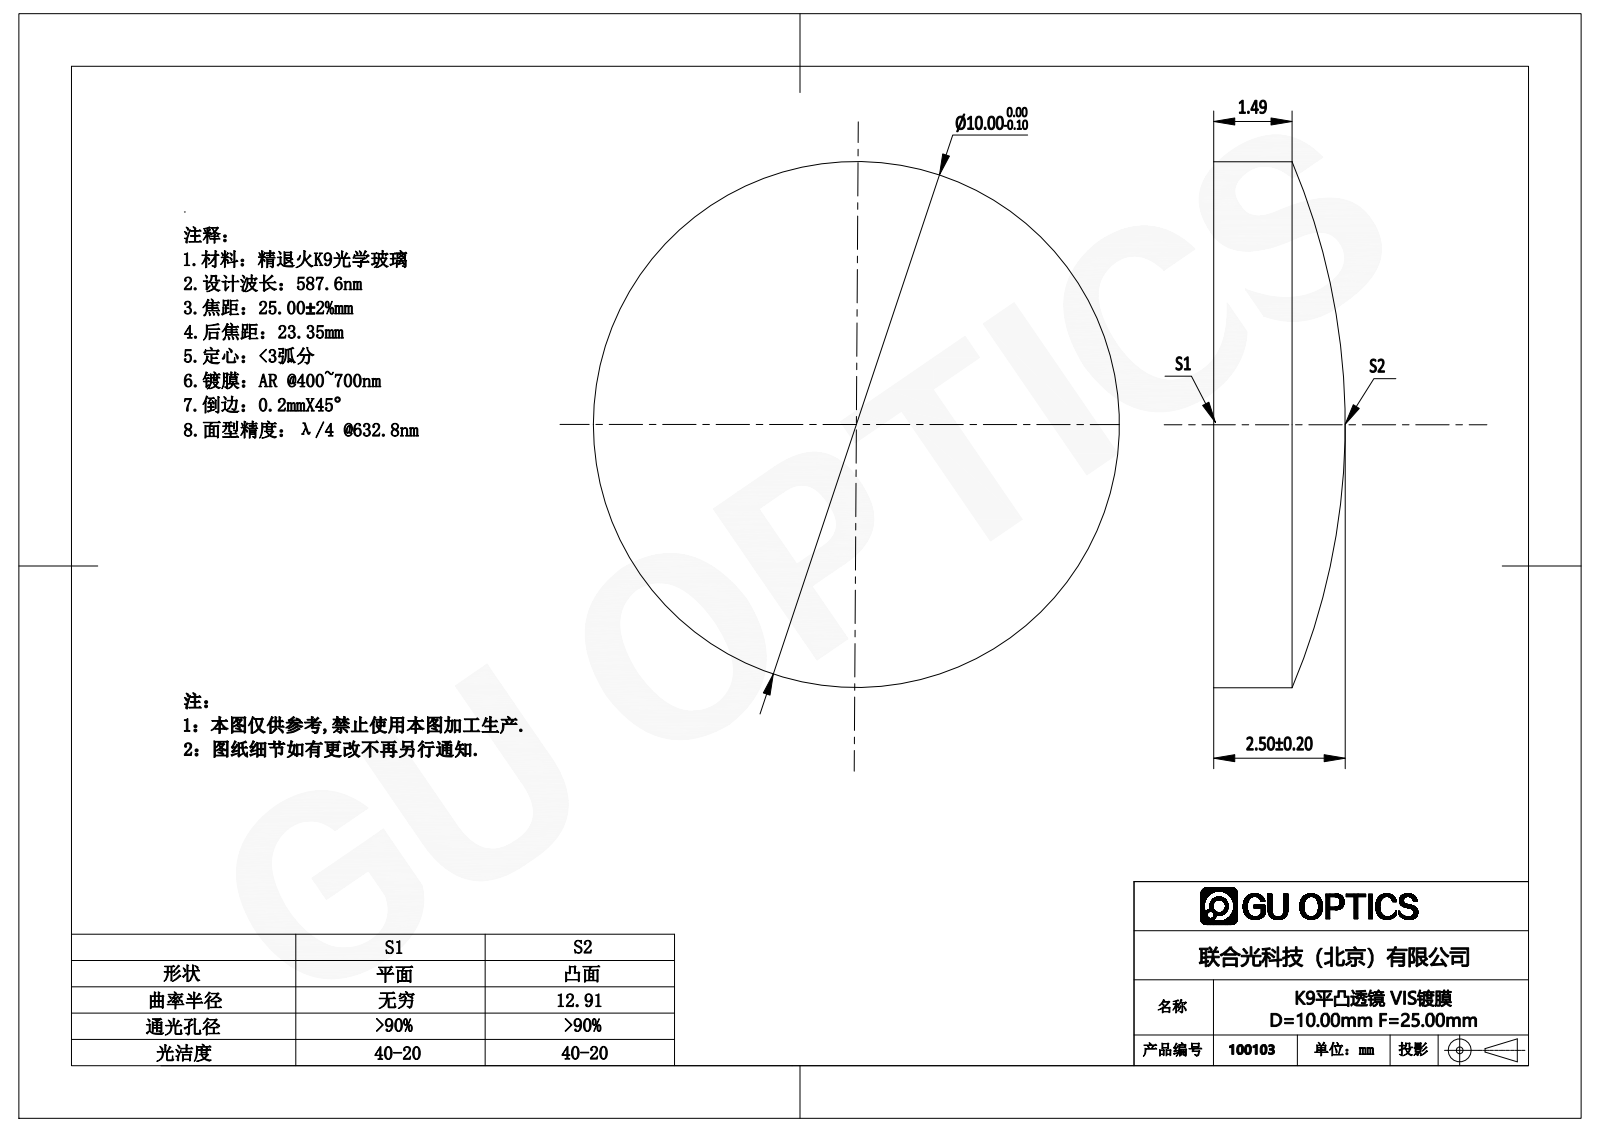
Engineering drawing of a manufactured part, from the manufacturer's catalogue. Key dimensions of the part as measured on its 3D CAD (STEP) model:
Part name (STEP PRODUCT): 100103
STEP written by: SolidWorks 2016 (AUTOMOTIVE_DESIGN)
Units: millimetres
Bodies: 1 solid, 5 faces (1 planar, 2 cylindrical, 2 other)
Overall size (bounding box): 10 × 10 × 2.5
Volume: 157 mm³ · Surface area: 207 mm²
Round bosses / shafts (diameter × count): ⌀10 ×1
